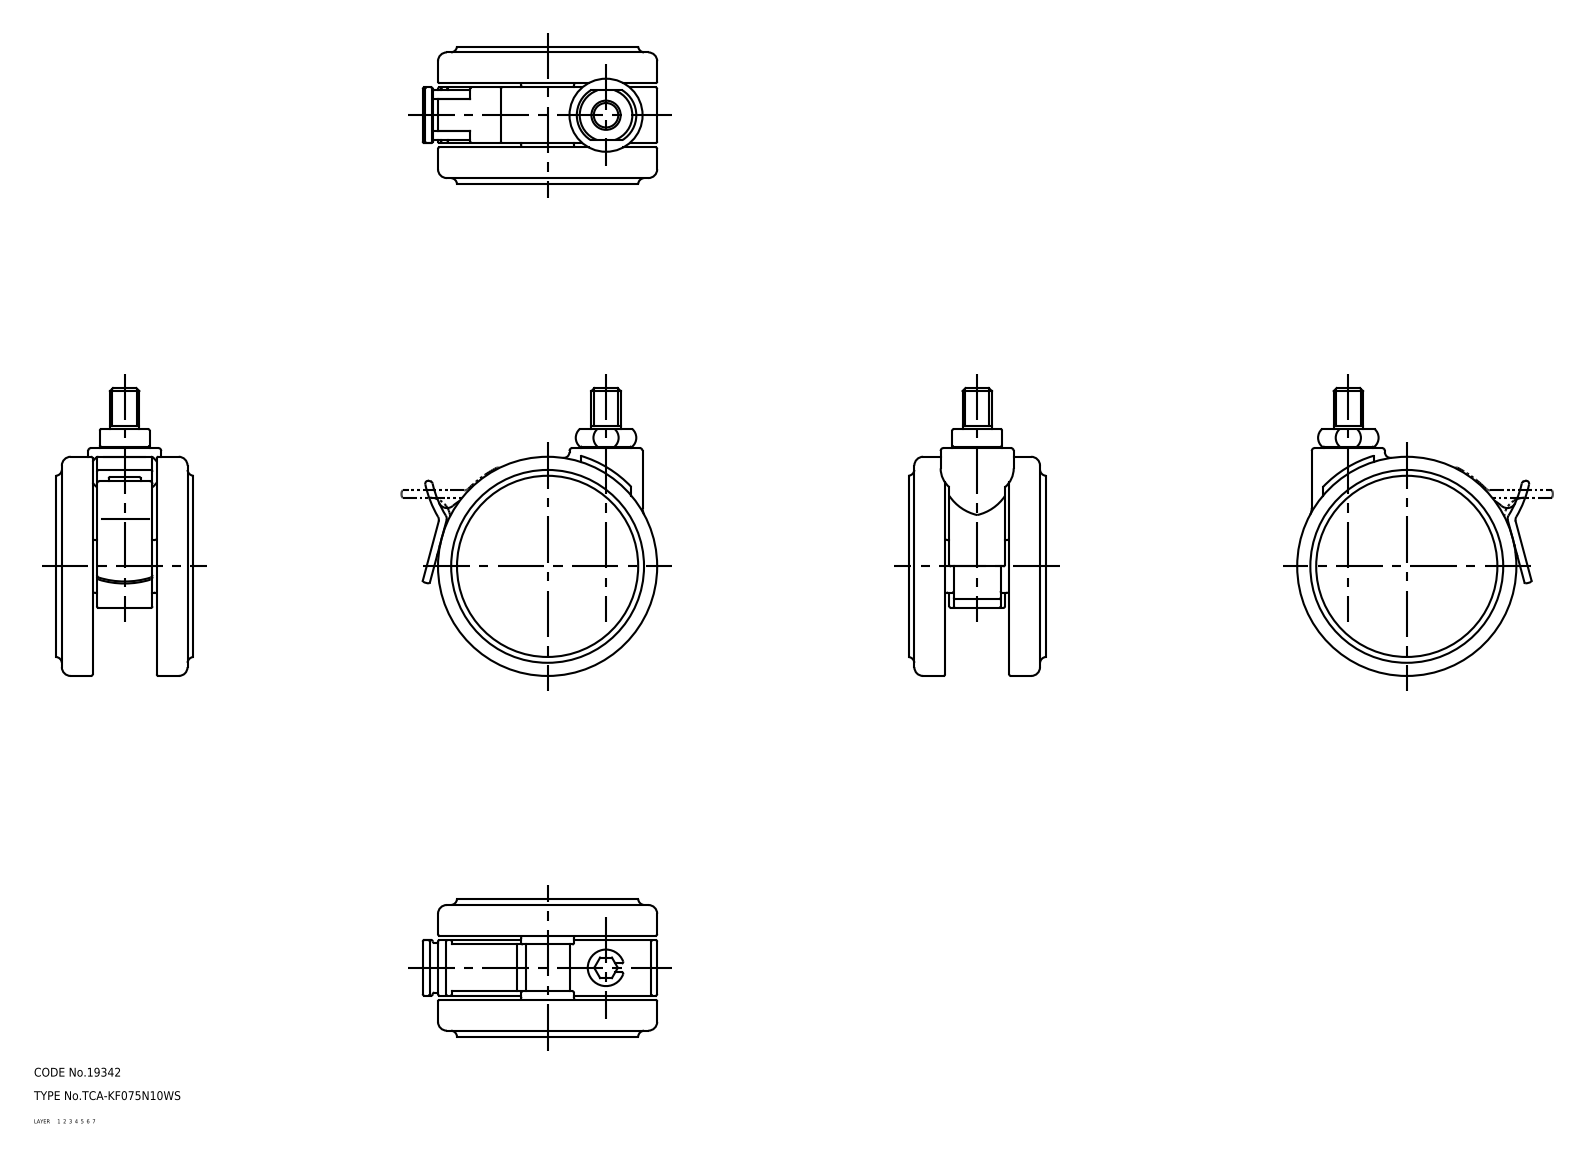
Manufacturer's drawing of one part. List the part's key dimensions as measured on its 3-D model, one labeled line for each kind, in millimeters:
Part name (STEP PRODUCT): TCA_KF075N10WS; wheel_mr; main shaft; wheel (+1 more)
STEP written by: SolidWorks 2015 (AUTOMOTIVE_DESIGN)
Units: millimetres
Bodies: 5 solids, 269 faces (62 planar, 107 cylindrical, 100 other)
Overall size (bounding box): 98.5 × 80.25 × 47
Volume: 155 448 mm³ · Surface area: 39 518 mm²
Round holes (diameter × count): ⌀6 ×1, ⌀43 ×1
Round bosses / shafts (diameter × count): ⌀75 ×1, ⌀25 ×1, ⌀18 ×1, ⌀17 ×1, ⌀12.5 ×1, ⌀10 ×1
Partial cylindrical surfaces — rounded edges, fillets, slot ends (radius × count): R0.5 ×43, R1 ×2, R2 ×2, R3 ×2, R35.5 ×2, R2.89 ×1, R7 ×1, R7.54 ×1
Main face-to-face distances: 12.5, 34.5, 1.5, 22, 3, 14, 19, 20.5, 47, 33
